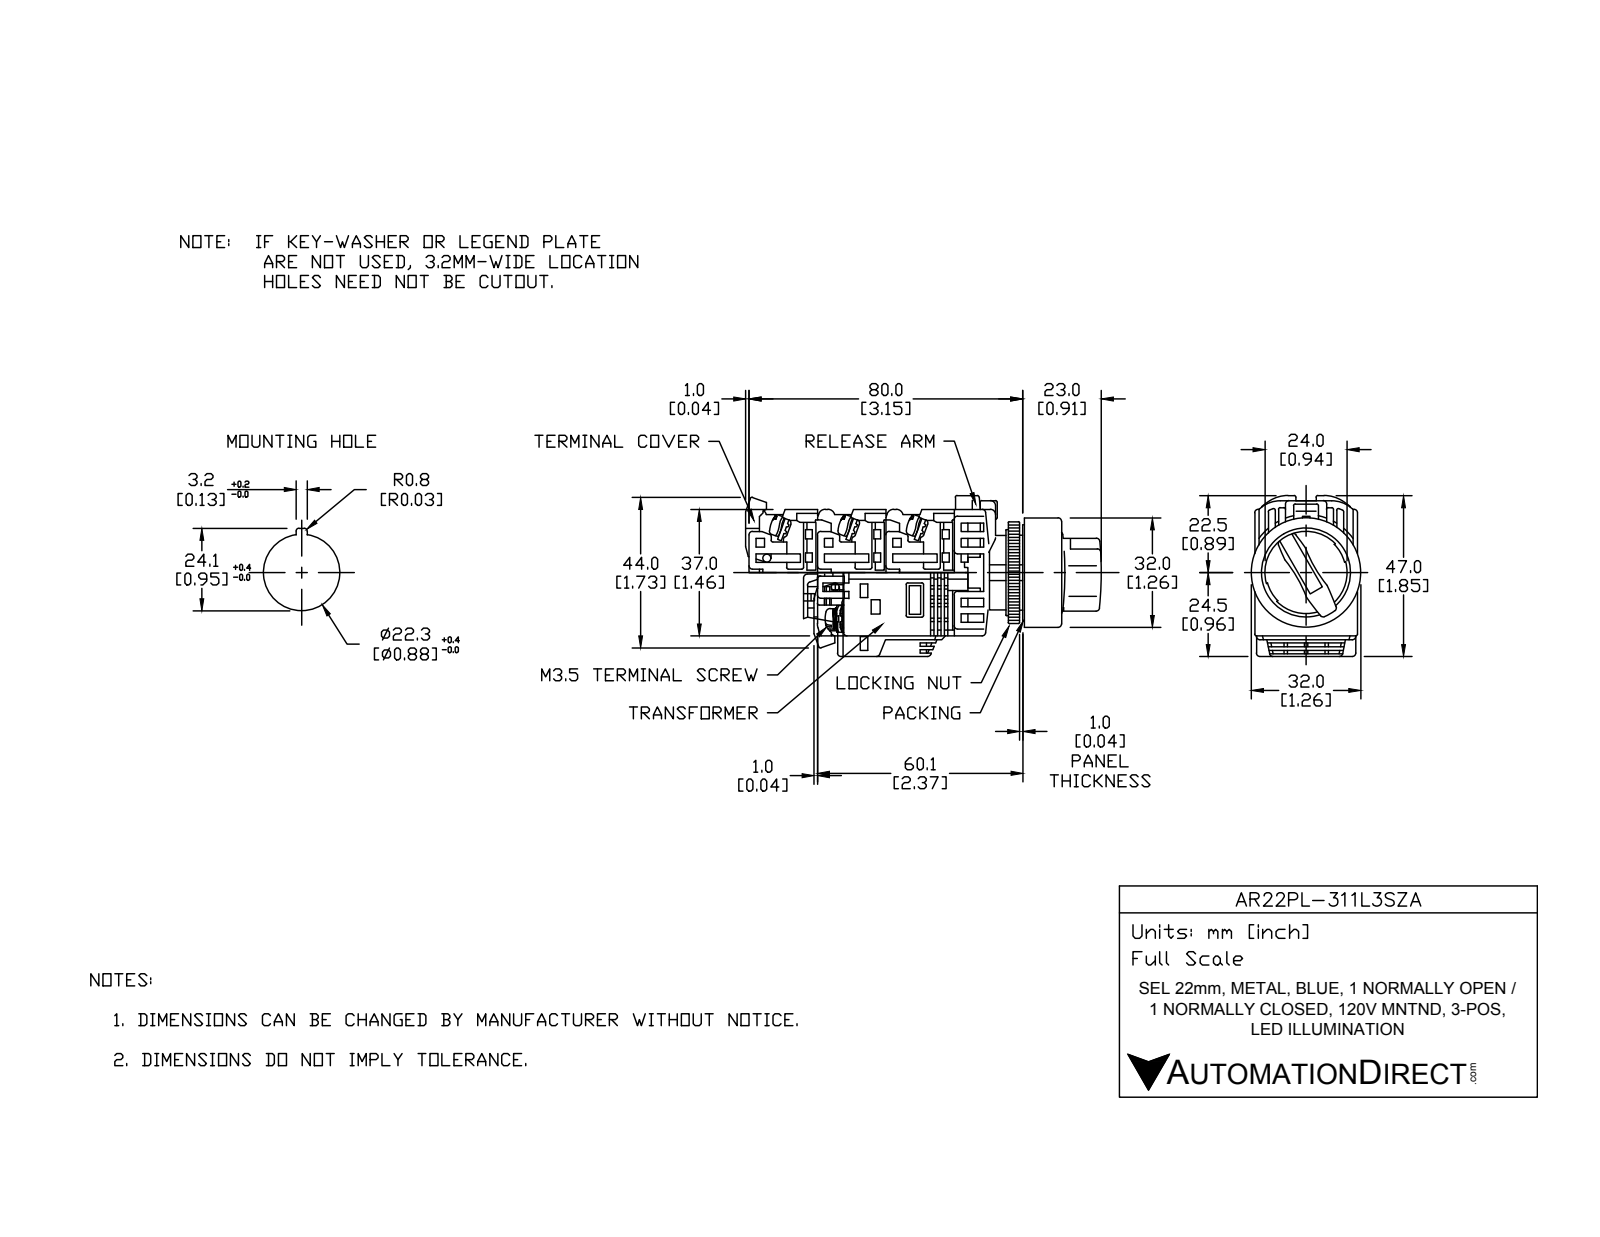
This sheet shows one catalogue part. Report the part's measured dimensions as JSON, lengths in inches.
{"part_name": "AR22PL-311L3SZA", "step_written_by": "SolidWorks 2017 (AUTOMOTIVE_DESIGN)", "units": "inches", "bodies": {"solids": 23, "faces": 556, "planar": 386, "cylindrical": 139, "other": 31}, "overall_size": [3.327, 1.725, 1.26], "volume_in3": 3.509, "surface_area_in2": 46.84, "round_holes": [[0.858, 1], [0.866, 1], [0.984, 1], [1.22, 1]], "round_bosses_or_shafts": [[0.197, 6], [1.26, 1], [1.201, 1], [1.173, 1], [0.945, 1], [0.856, 1], [0.669, 1]], "partial_cylinders_radius": [[0.02, 48], [0.069, 8], [0.039, 6], [0.197, 4], [0.157, 2], [0.472, 1], [0.653, 1], [0.693, 1]], "face_to_face_distances": [0.039, 0.709, 0.787, 1.142, 0.118, 1.575, 1.122, 2.697, 0.079, 0.394]}
